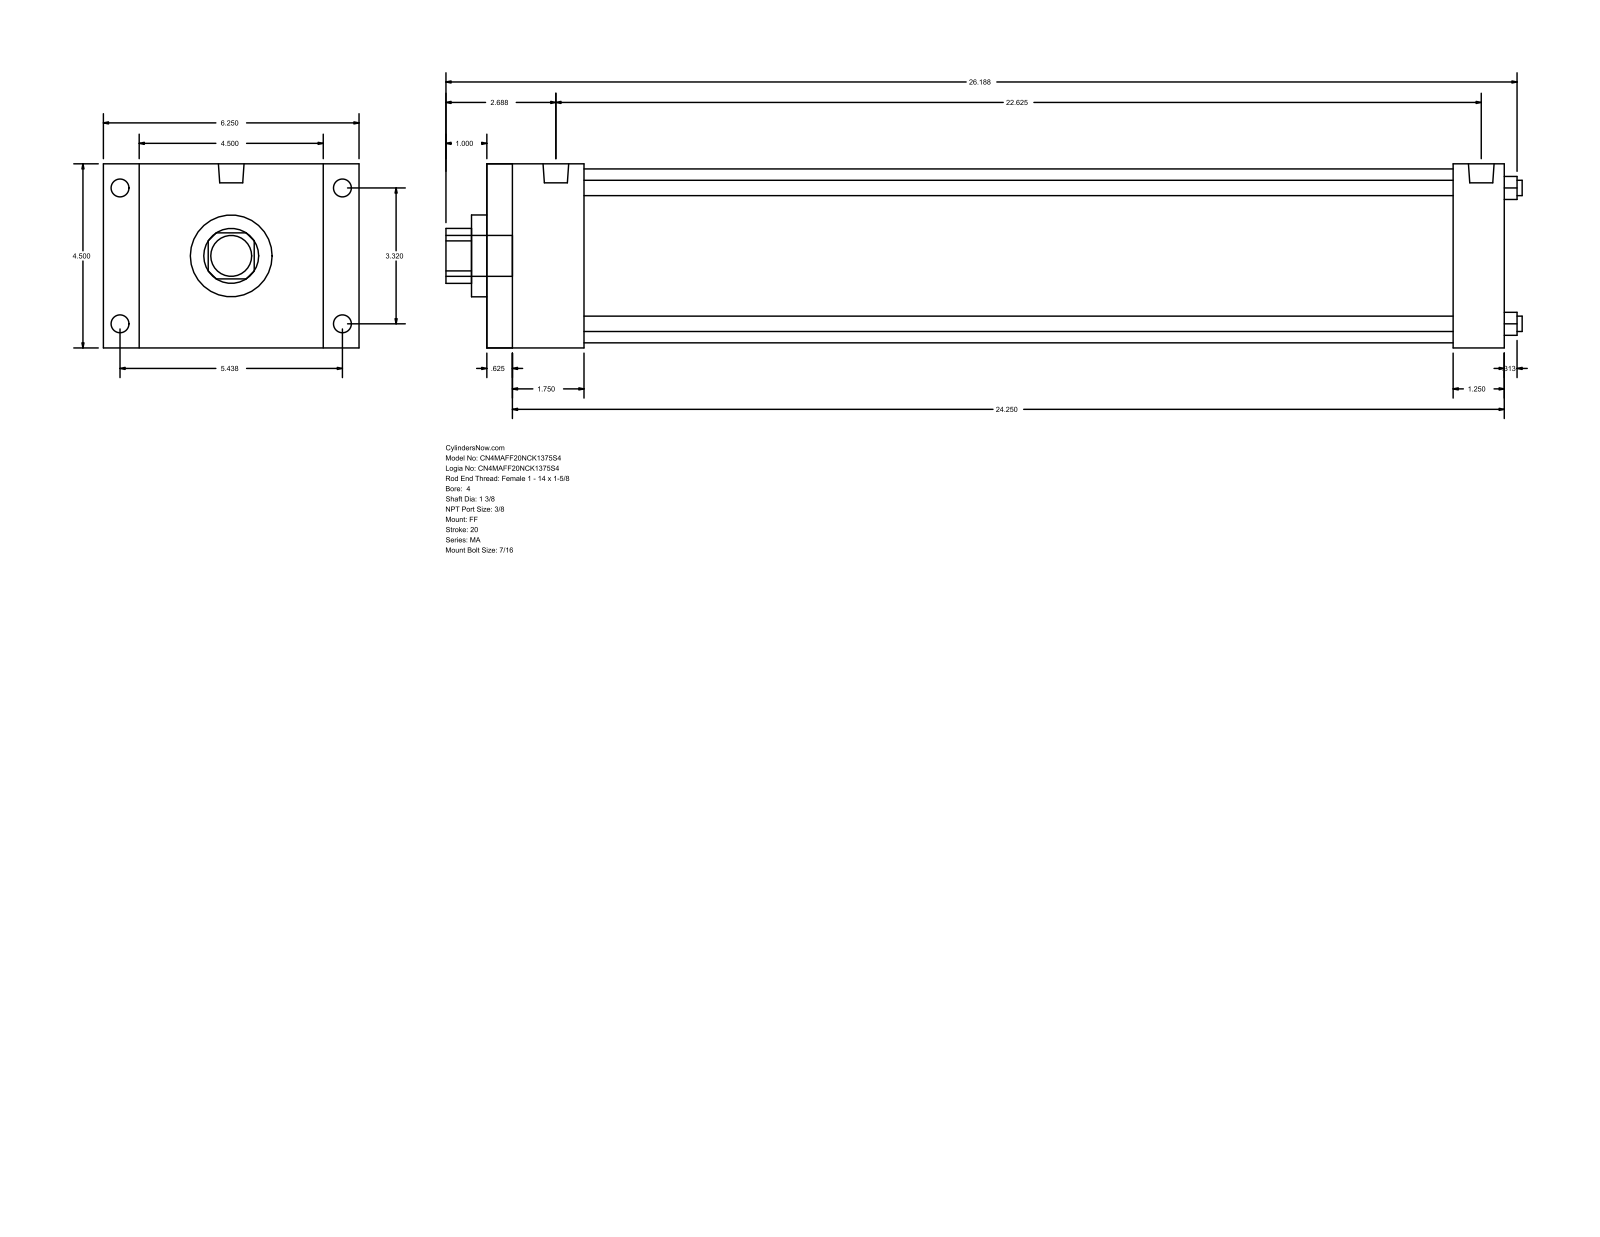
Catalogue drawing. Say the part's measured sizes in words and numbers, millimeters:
The part is named "MA_FF__0400_1.375". Its 3-D file was written by "GSSL Pune (CONFIG_CONTROL_DESIGN)". It is 0 solids with 92 faces: 64 planar, 28 cylindrical and 0 other. Overall it measures 668.34 by 158.75 by 114.3 millimeters. Round holes: 4 of diameter 9.53, 1 of diameter 34.92, 1 of diameter 50.8, 1 of diameter 107.95. Round bosses or shafts: 8 of diameter 11.11, 2 of diameter 15.93, 1 of diameter 25.4. Partial cylindrical surfaces (rounded edges, fillets, slot ends): 1 of radius 17.06. The main face-to-face distances are 114.3, 631.83, 15.87, 615.96, 22.23, 136.53, 600.08, 584.21, 31.75, 60.32. The hole center spacings are 59.62, 84.32, 119.25.
